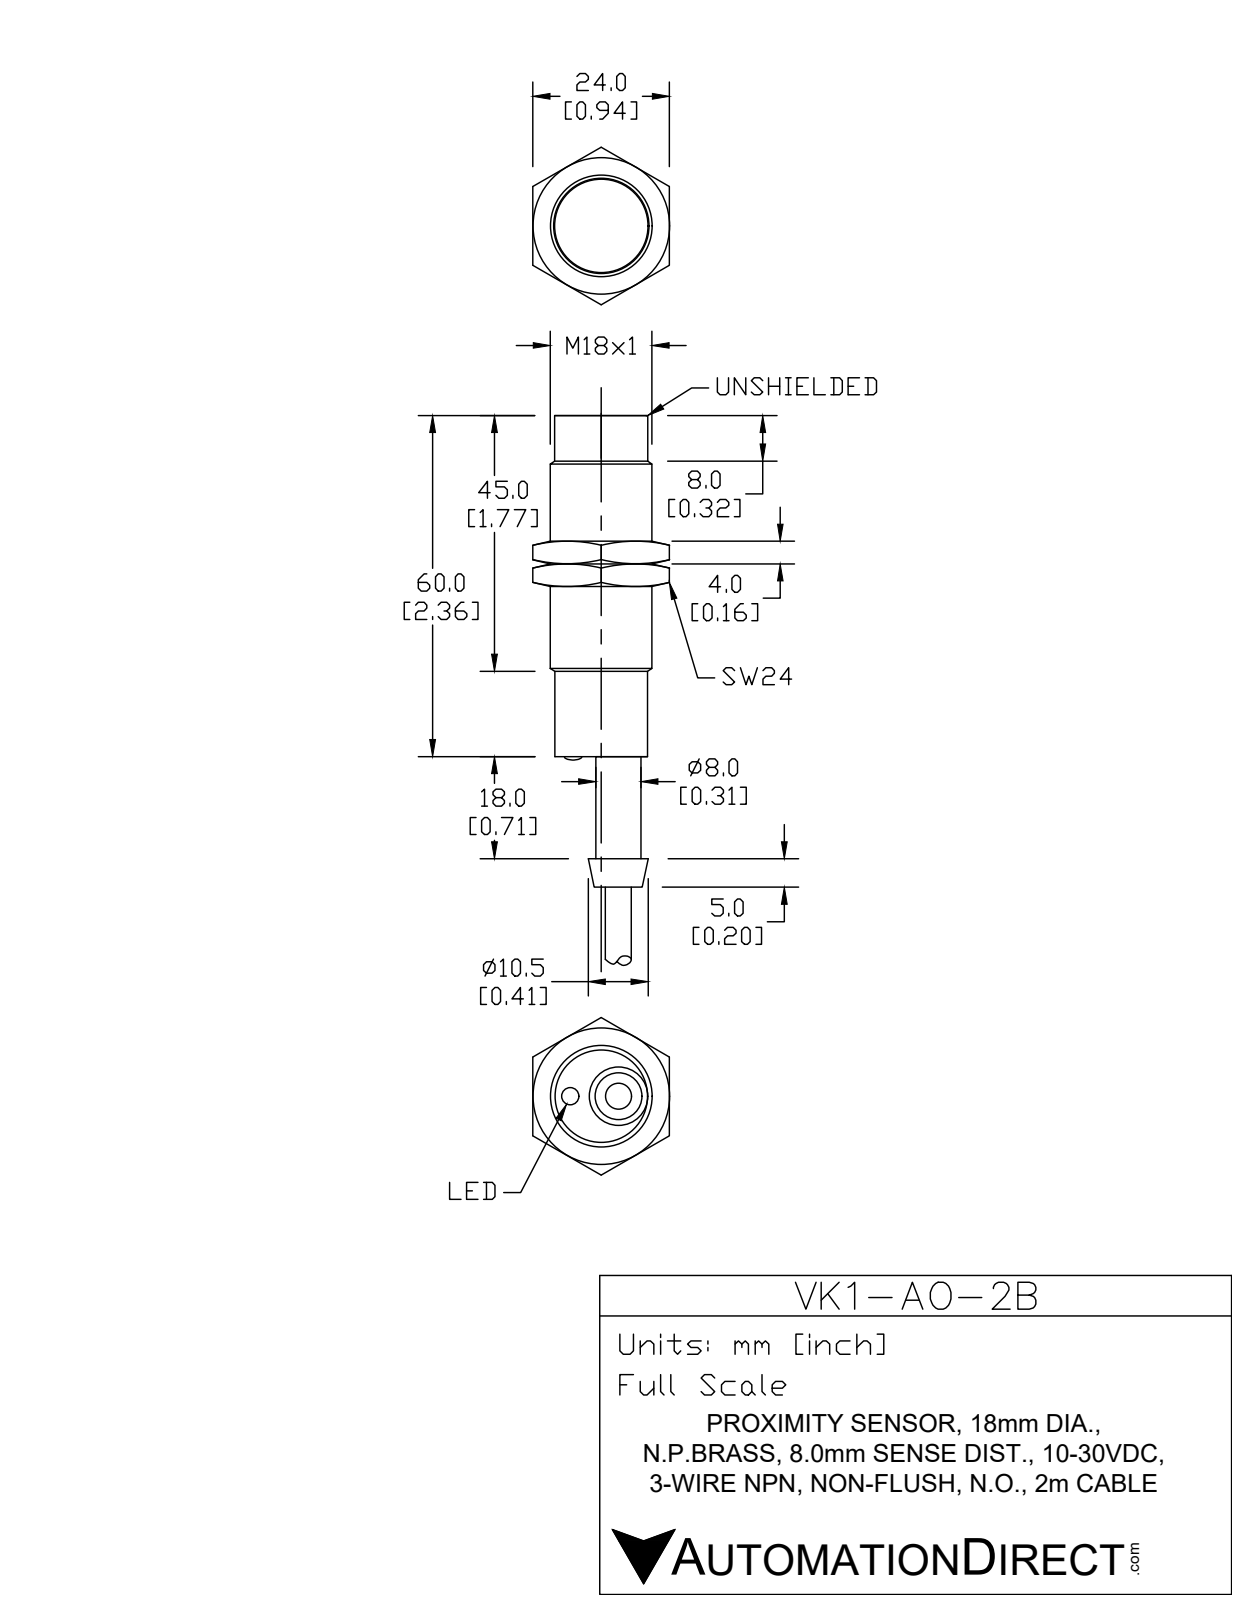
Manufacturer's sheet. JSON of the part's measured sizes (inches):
{"part_name": "VK1-A0-2B", "step_written_by": "SolidWorks 2017 (AUTOMOTIVE_DESIGN)", "units": "inches", "bodies": {"solids": 4, "faces": 43, "planar": 14, "cylindrical": 15, "other": 14}, "overall_size": [4.409, 0.709, 0.709], "volume_in3": 0.97, "surface_area_in2": 8.891, "round_holes": [[0.185, 1]], "round_bosses_or_shafts": [[0.709, 1], [0.65, 1], [0.626, 1], [0.409, 1], [0.315, 1]], "partial_cylinders_radius": [[0.319, 1]], "face_to_face_distances": [1.654, 0.315, 1.969, 2.047, 2.362, 0.394, 2.835, 2.52, 0.866, 0.472]}
